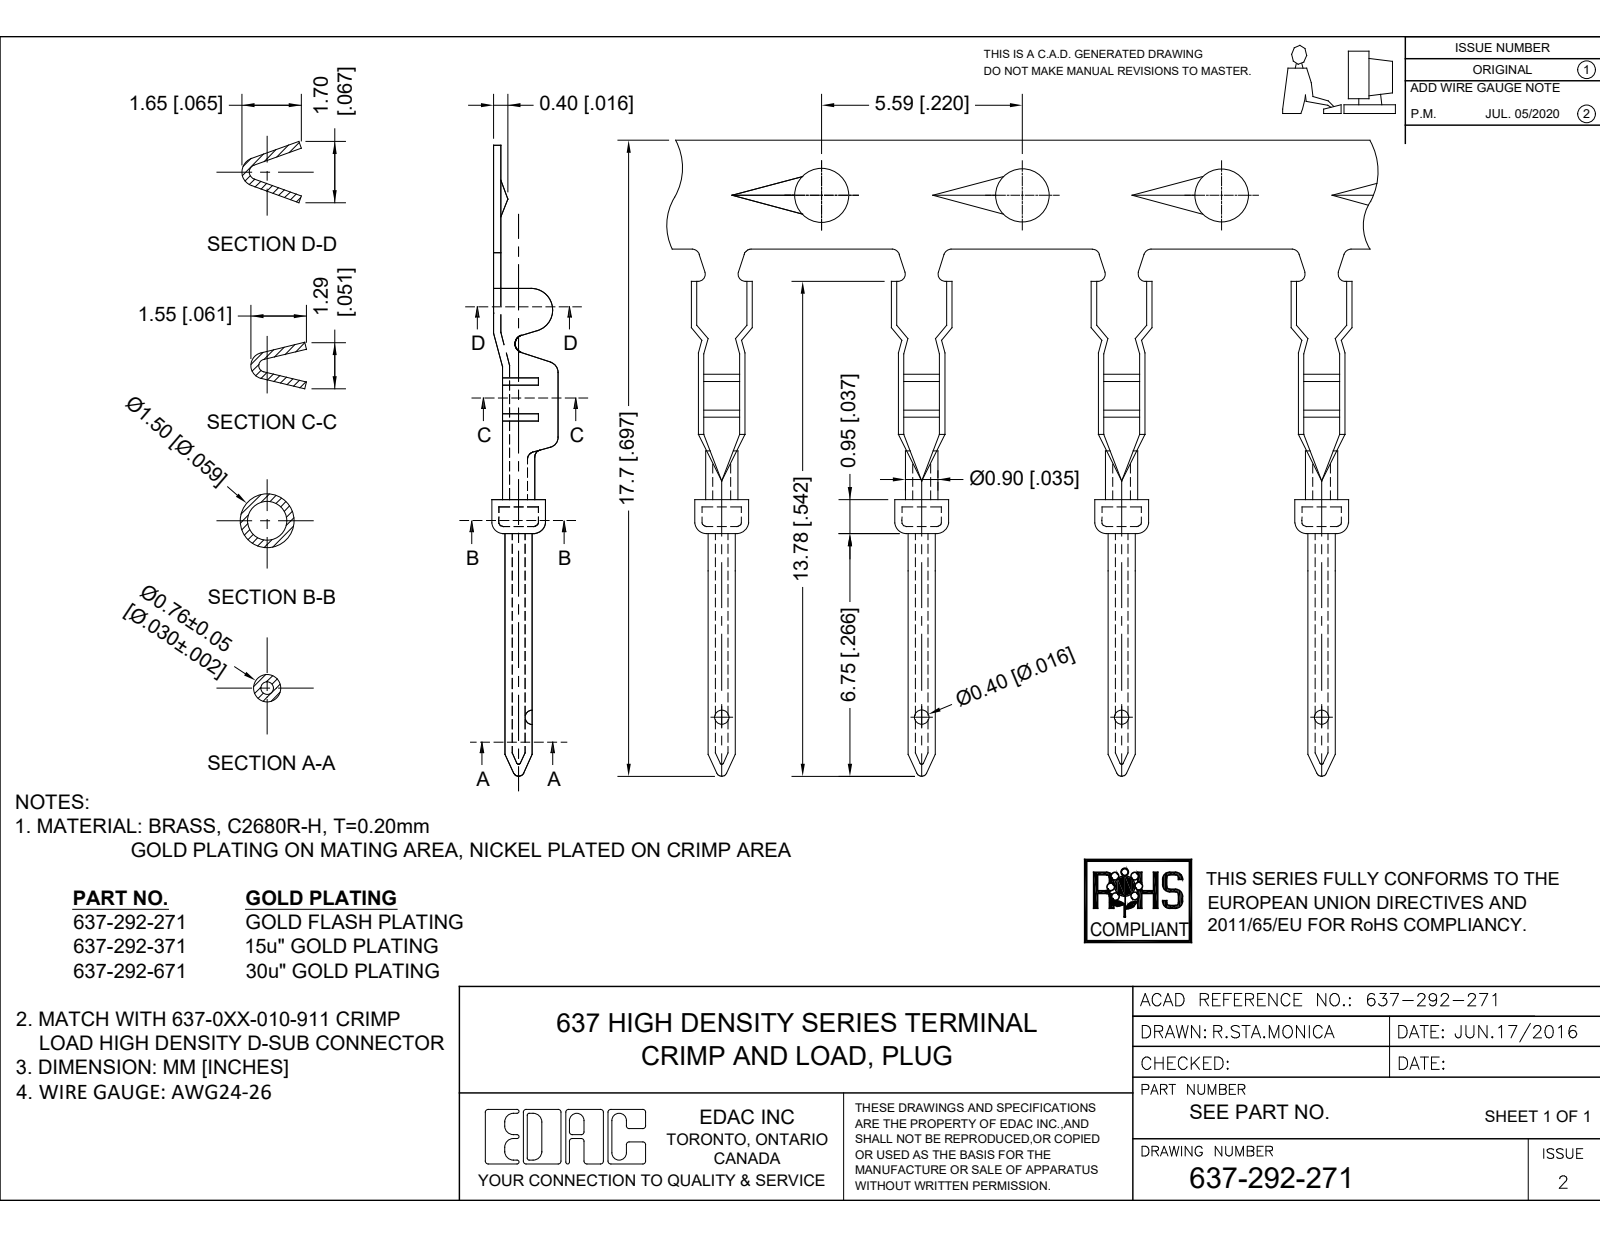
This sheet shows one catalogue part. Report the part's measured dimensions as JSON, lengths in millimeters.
{"part_name": "637-292-271", "step_written_by": "SolidWorks 2020 (AUTOMOTIVE_DESIGN)", "units": "millimeters", "bodies": {"solids": 1, "faces": 112, "planar": 56, "cylindrical": 26, "other": 30}, "overall_size": [13.96, 1.84, 1.7], "volume_mm3": 7, "surface_area_mm2": 75, "round_holes": [[0.36, 1], [0.4, 1], [0.57, 1], [1.1, 1]], "round_bosses_or_shafts": [[1.5, 1], [0.97, 1], [0.76, 1]], "partial_cylinders_radius": [[0.6, 4], [0.14, 1], [0.17, 1], [0.2, 1], [0.25, 1], [0.34, 1], [0.36, 1], [0.4, 1]], "face_to_face_distances": [0.76, 0.96, 7.01, 6.81, 6.05, 0.56, 6.25, 3.11, 2.35, 4.11]}
